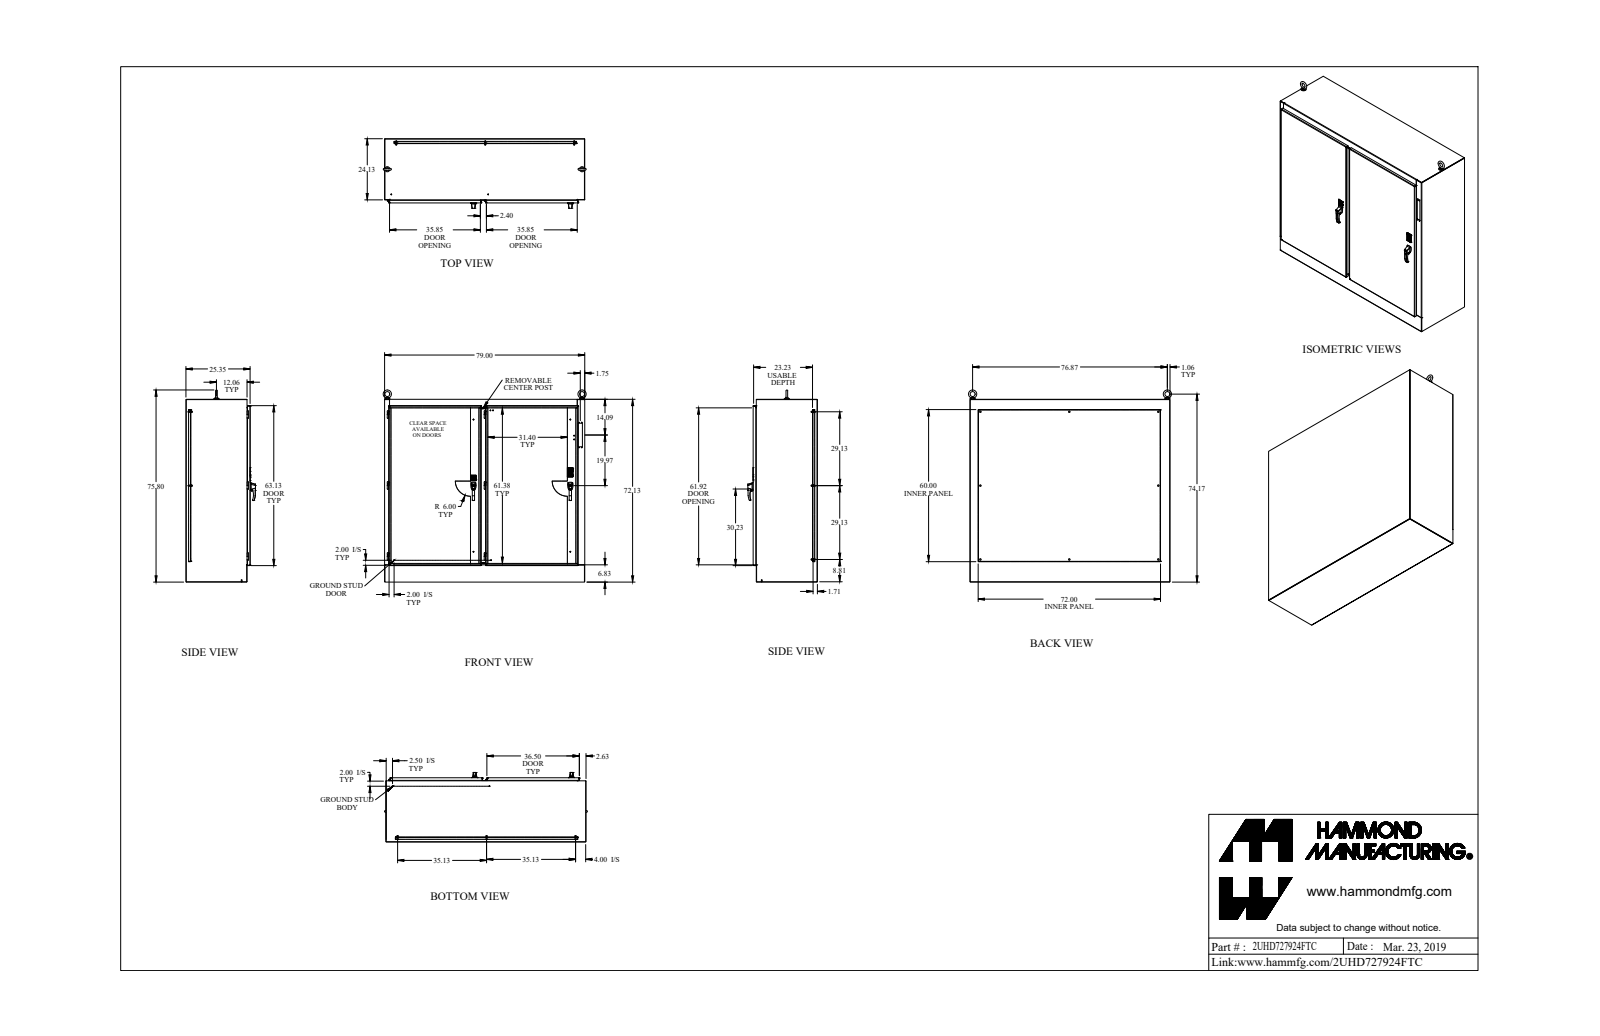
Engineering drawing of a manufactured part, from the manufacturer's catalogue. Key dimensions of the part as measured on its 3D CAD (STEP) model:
Part name (STEP PRODUCT): 2UHD727924FTC
STEP written by: SolidWorks 2018 (AUTOMOTIVE_DESIGN)
Units: inches
Bodies: 216 solids, 3050 faces (1766 planar, 898 cylindrical, 386 other)
Overall size (bounding box): 80.122 × 75.799 × 27.466
Volume: 4 989 in³ · Surface area: 53 755 in²
Round holes (diameter × count): ⌀0.196 ×12, ⌀0.281 ×11, ⌀0.307 ×11, ⌀0.25 ×8, ⌀0.35 ×8, ⌀0.313 ×6, ⌀0.445 ×5, ⌀0.255 ×4, ⌀0.257 ×4, ⌀0.282 ×4, ⌀0.375 ×4, ⌀0.39 ×4
Round bosses / shafts (diameter × count): ⌀0.25 ×19, ⌀1 ×12, ⌀0.65 ×9, ⌀0.375 ×9, ⌀0.33 ×9, ⌀0.281 ×8, ⌀0.75 ×6, ⌀0.53 ×6
Partial cylindrical surfaces — rounded edges, fillets, slot ends (radius × count): R0.125 ×56, R0.06 ×51, R0.5 ×38, R0.017 ×32, R0.185 ×30, R0.03 ×28, R0.032 ×12, R0.09 ×12
Main face-to-face distances: 0.125, 0.072, 23.431, 25.369, 25.243, 1.937, 1.812, 1.865, 1.74, 23.503
Hole centre spacings: 38.25, 1, 1.126, 1.287, 24.937, 26.063, 26.07, 27.188
